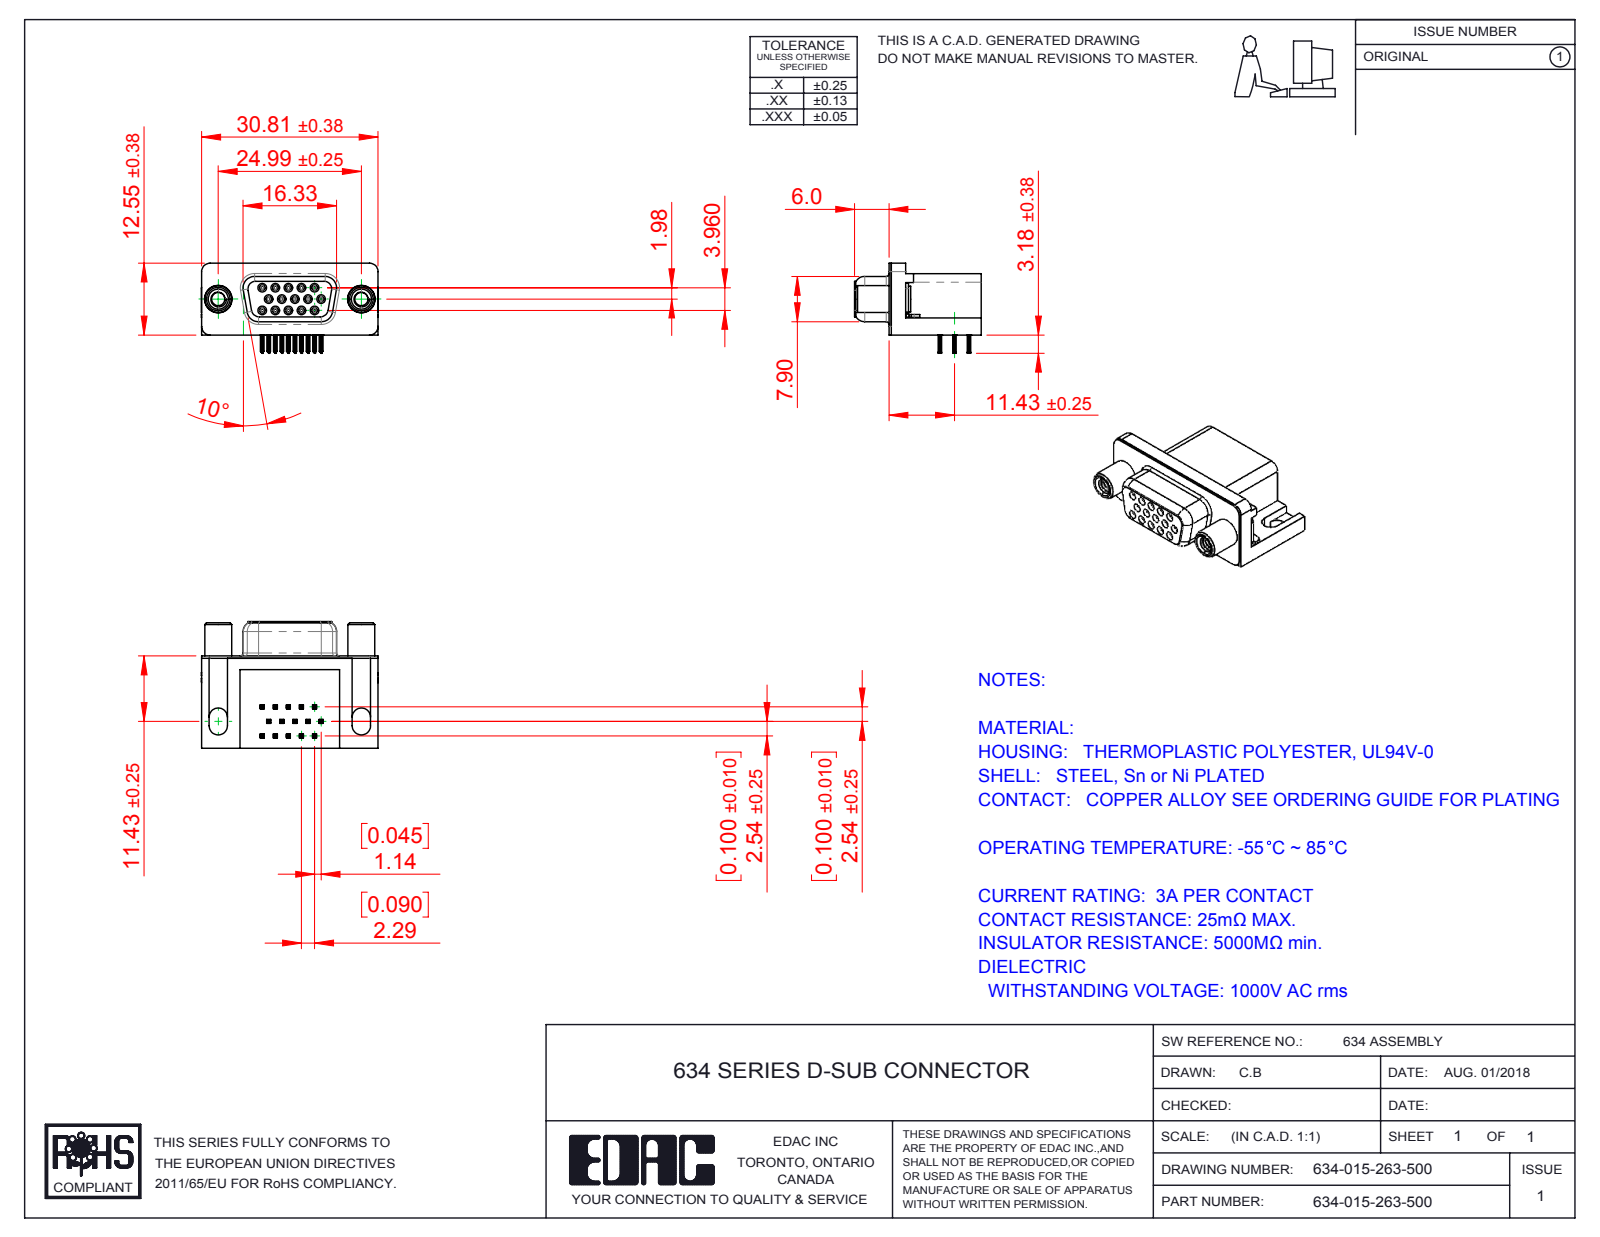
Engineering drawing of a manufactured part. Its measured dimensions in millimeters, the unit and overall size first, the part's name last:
Units: millimetres
Overall size (bounding box): 30.89 × 22.1 × 15.73
Round holes (diameter × count): ⌀0.8 ×15, ⌀0.9 ×15, ⌀2.3 ×2, ⌀3.1 ×2, ⌀4 ×2, ⌀4.8 ×2, ⌀5 ×2
Round bosses / shafts (diameter × count): ⌀1.2 ×15, ⌀4.9 ×2, ⌀4.7 ×2, ⌀4.5 ×2, ⌀3.85 ×2
Partial cylindrical surfaces — rounded edges, fillets, slot ends (radius × count): R0.1 ×120, R0.15 ×60, R0.35 ×30, R1 ×19, R0.34 ×15, R1.35 ×8, R1.6 ×8, R1.5 ×7
Main face-to-face distances: 0.4, 10.35, 15.7, 16.1, 2.5, 6.7, 2.9, 0.35, 10.7, 13.2
Hole centre spacings: 2.29, 2.28, 3.96, 4.57, 6.05, 3.97, 4.58, 6.86
Volume: 4 596 mm³ · Surface area: 6 477 mm²
Bodies: 21 solids, 2411 faces (1058 planar, 603 cylindrical, 750 other)
Part name (STEP PRODUCT): 634-015-263-500; Round Threaded Standoff; Contact Middle; Contact Bottom (+4 more)
STEP written by: SolidWorks 2016 (CONFIG_CONTROL_DESIGN)
